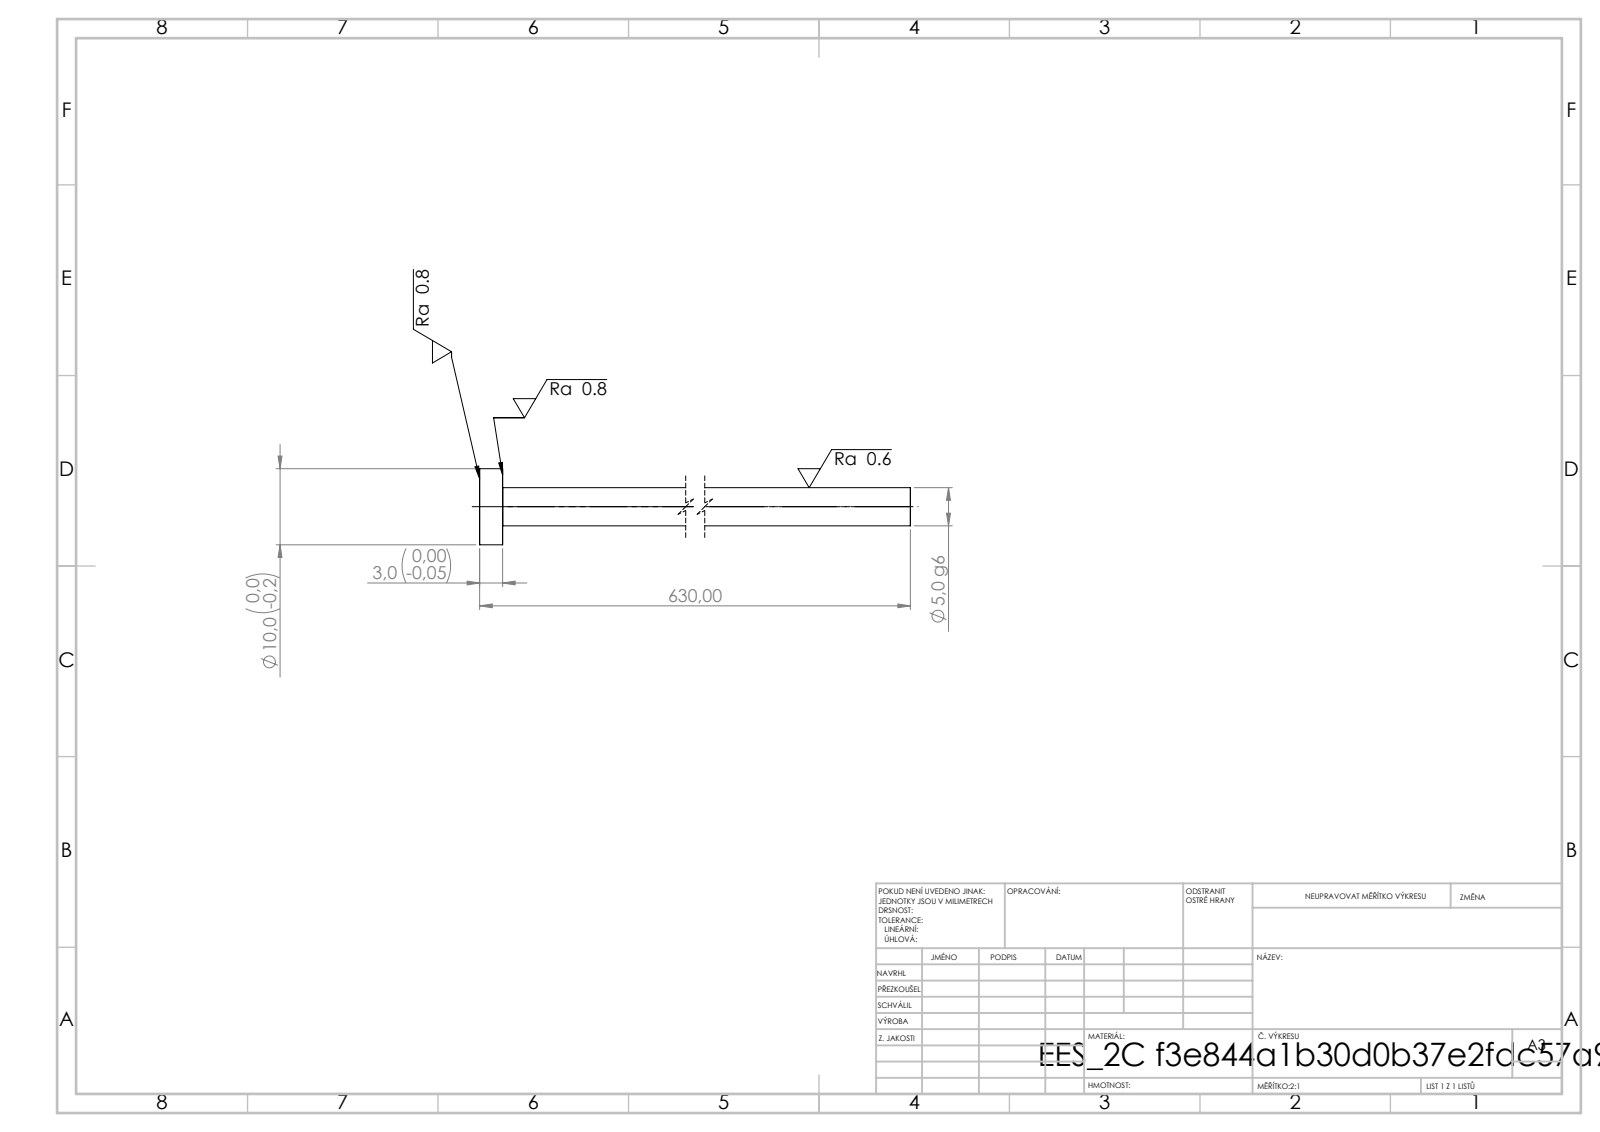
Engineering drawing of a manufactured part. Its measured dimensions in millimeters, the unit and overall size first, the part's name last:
Units: millimetres
Overall size (bounding box): 630 × 10 × 10
Round bosses / shafts (diameter × count): ⌀10 ×1, ⌀5 ×1
Main face-to-face distances: 3, 630, 627
Volume: 12 547 mm³ · Surface area: 10 100 mm²
Bodies: 1 solid, 7 faces (3 planar, 4 cylindrical, 0 other)
STEP written by: SolidWorks 2019 (CONFIG_CONTROL_DESIGN)
